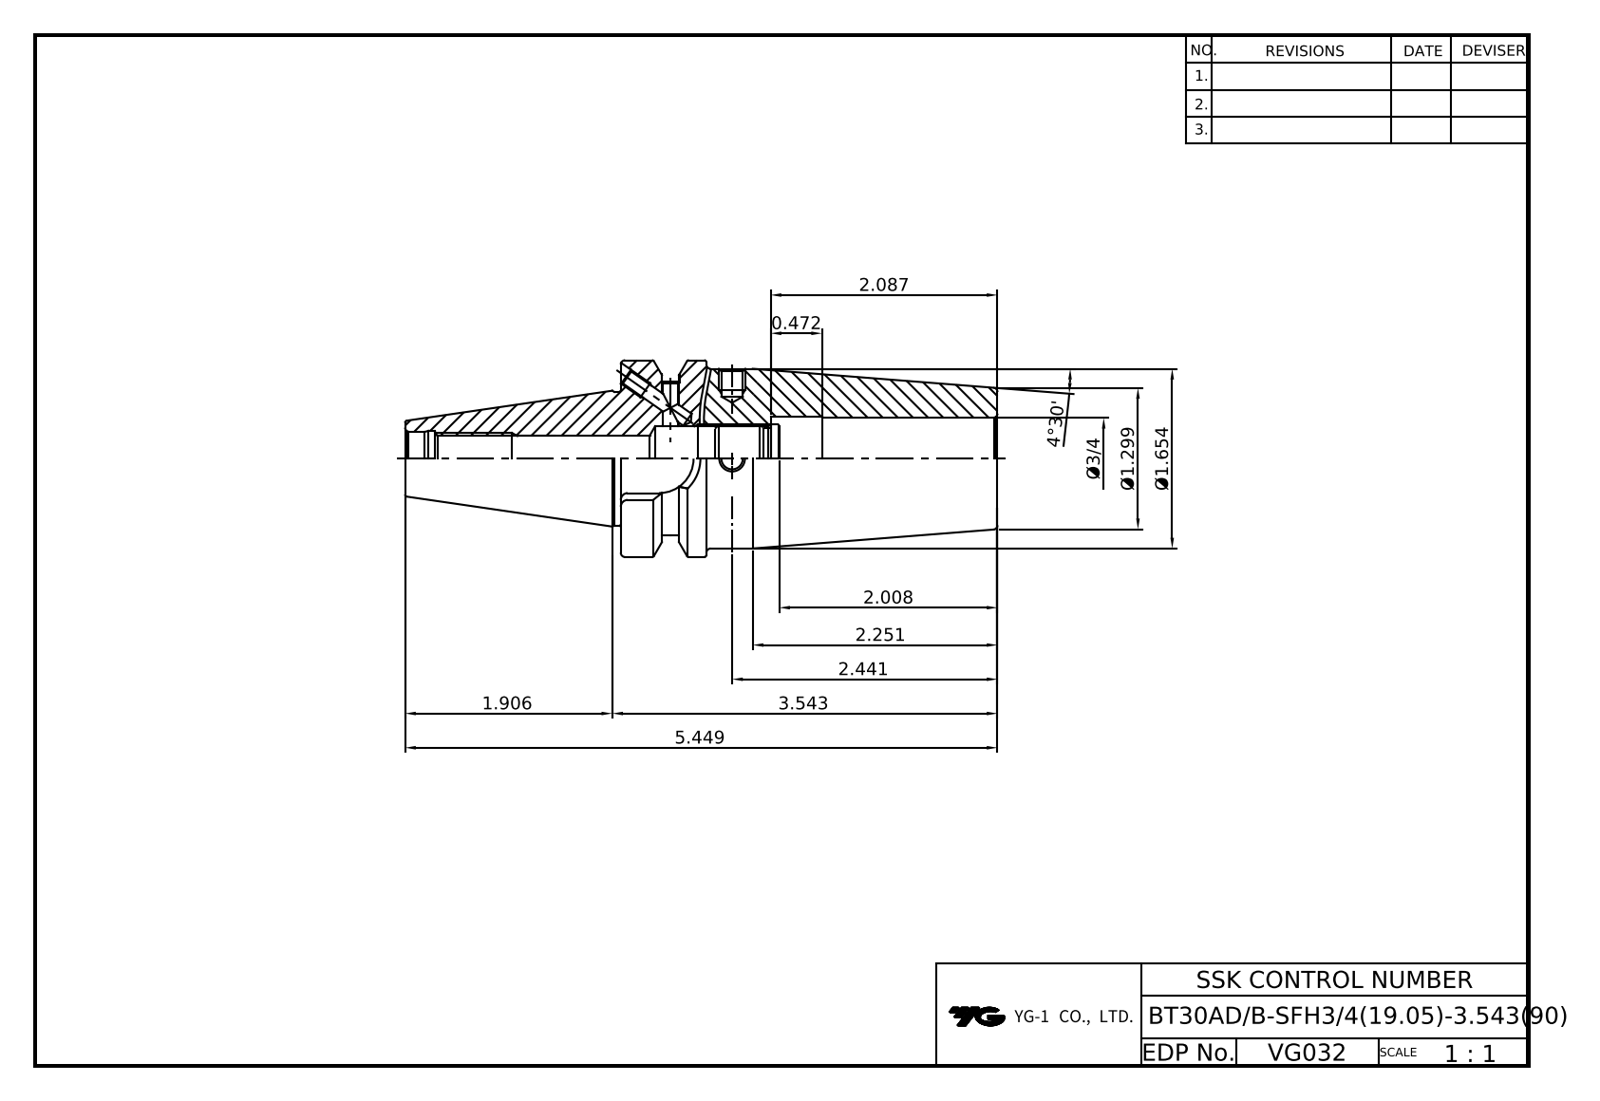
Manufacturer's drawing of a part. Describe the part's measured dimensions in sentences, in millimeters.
The part is named "LO-BT30-SFH19.05-3.54". Its 3-D file was written by "Autodesk Inventor 2025 (AUTOMOTIVE_DESIGN)". It is 1 solid with 50 faces: 17 planar, 15 cylindrical and 18 other. Overall it measures 138.4 by 46 by 46 millimeters. Its volume is 105 996 cubic millimeters and its surface area 23 971 square millimeters. Round holes: 1 of diameter 10.11, 1 of diameter 12.5, 1 of diameter 13.1, 1 of diameter 14.92, 1 of diameter 19.05, 1 of diameter 20.25. Round bosses or shafts: 1 of diameter 46, 1 of diameter 42, 1 of diameter 31.2. Partial cylindrical surfaces (rounded edges, fillets, slot ends): 1 of radius 8.05, 1 of radius 18.8. The main face-to-face distances are 88, 32.6, 34, 54, 16.1, 20, 14, 68, 50.4, 70.4.
